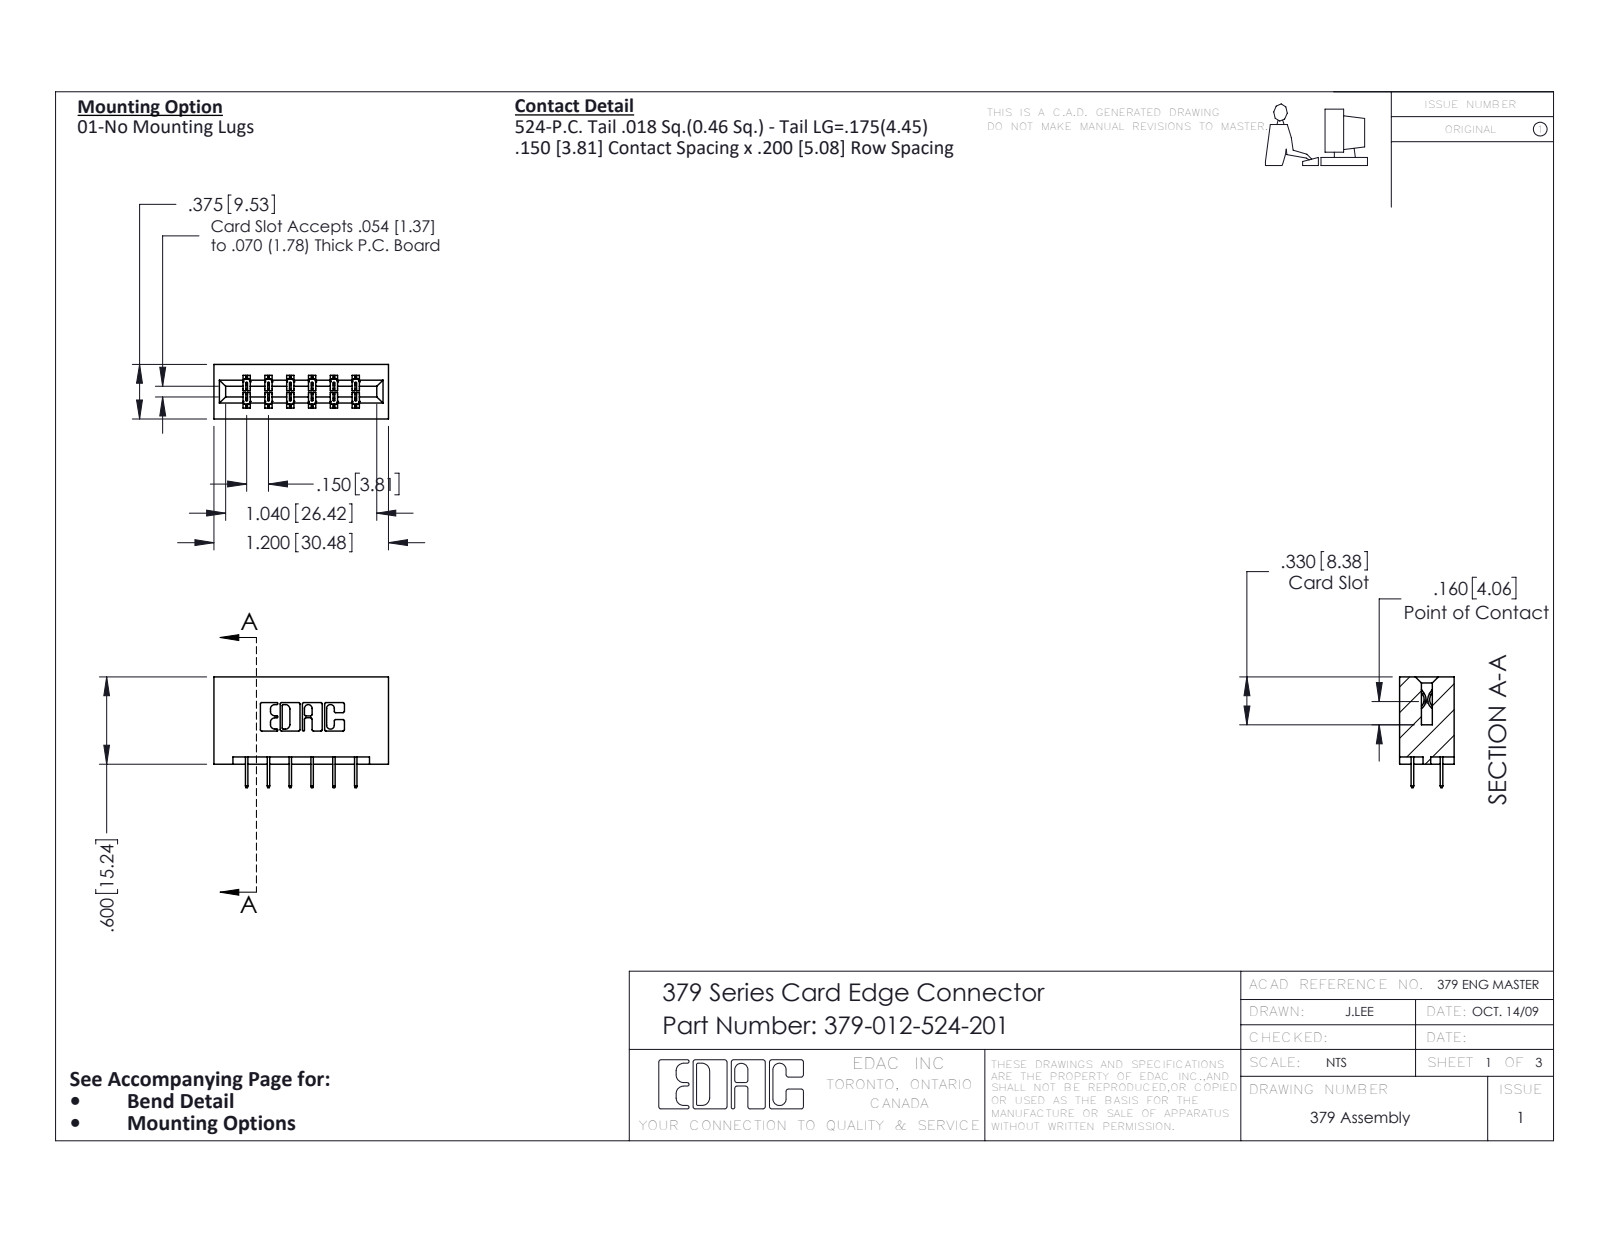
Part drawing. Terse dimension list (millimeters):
name: 345-292-001_345-293-124; 379-012-524-201; 379 Part_Lugless
written by: SolidWorks 2016 (CONFIG_CONTROL_DESIGN)
unit: mm
bodies: 13 solids, 778 faces (570 planar, 208 cylindrical, 0 other)
size: 30.5 × 19.4 × 9.5
volume: 3 510 mm³; area: 3 601 mm²
rounds: 22× R0.3, 18× R0.2, 6× R0.2, 6× R0.8, 3× R0.7, 2× R0.4, 2× R0.6, 2× R0.6
face distances: 7.6, 5.1, 3.8, 1.3, 9.5, 2.5, 1.9, 14, 6.4, 8.9
